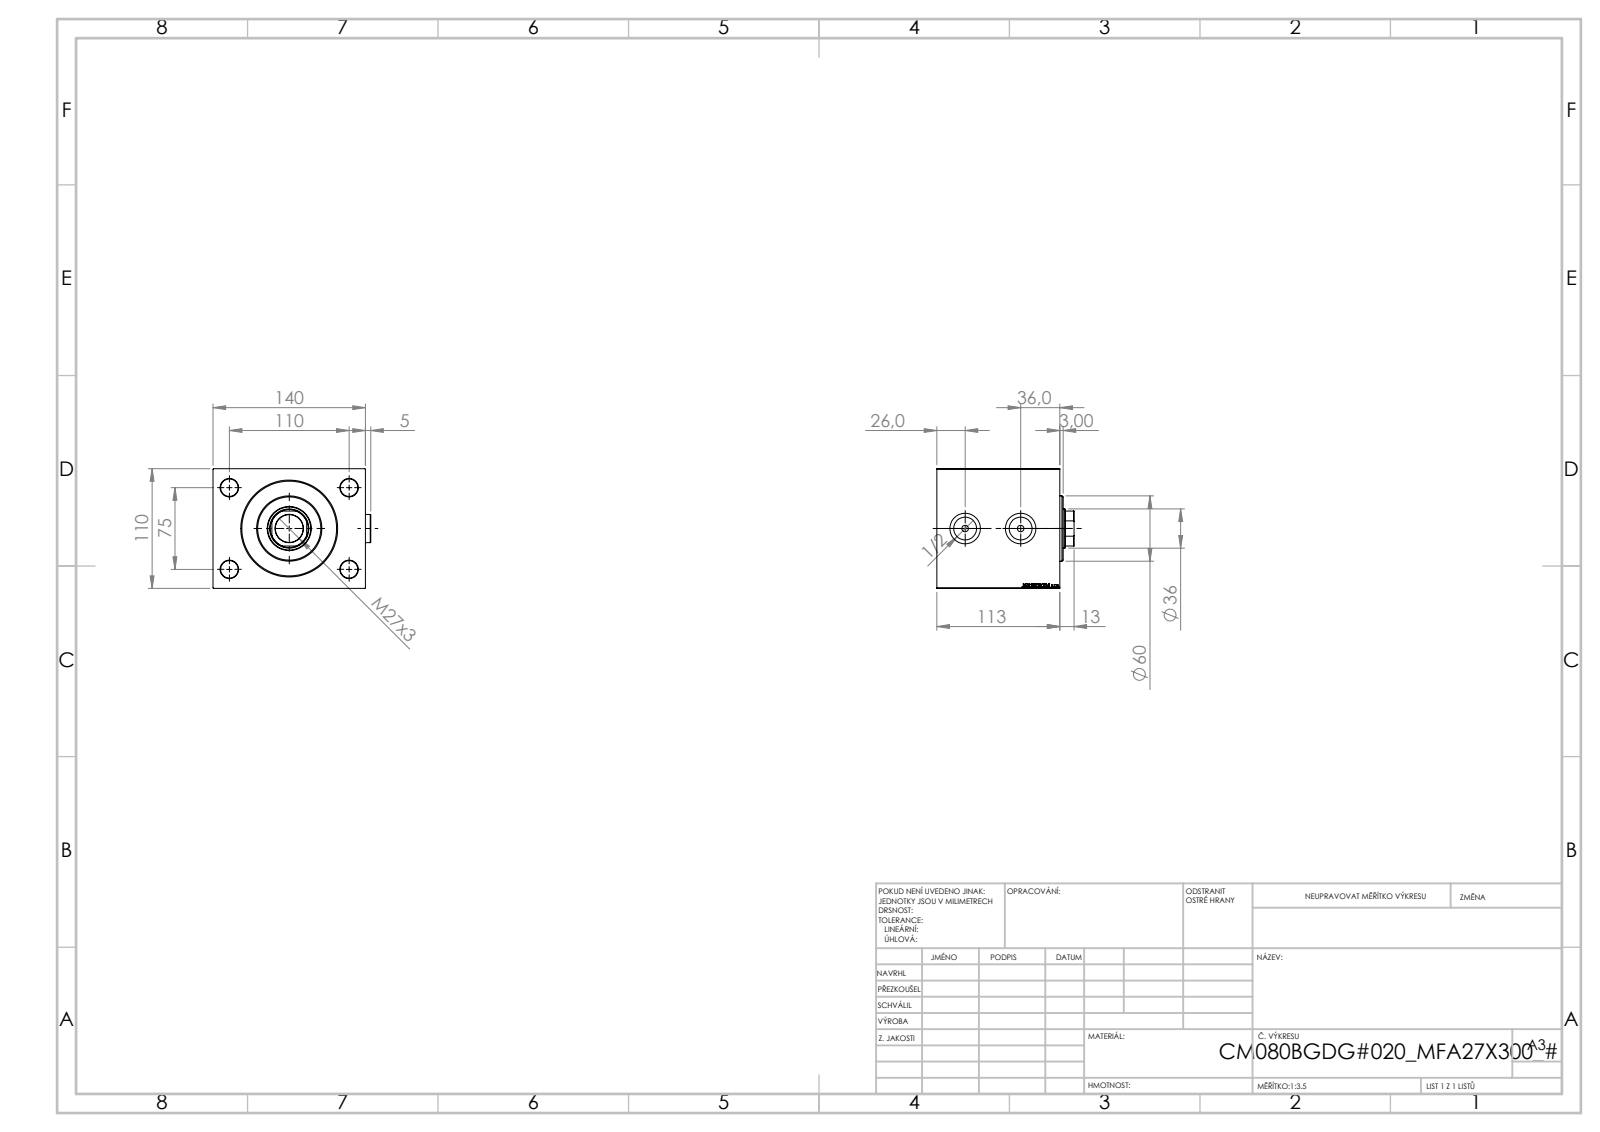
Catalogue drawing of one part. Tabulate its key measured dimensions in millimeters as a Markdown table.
| quantity | value |
| --- | --- |
| part name | V450CM_VC_B; V450CM_B_Body; Zatka_OIL_PORT; V450CM_B_VCP |
| STEP written by | SolidWorks 2019 (CONFIG_CONTROL_DESIGN) |
| units | millimeters |
| bodies | 5 solids, 936 faces (436 planar, 70 cylindrical, 430 other) |
| overall size | 144.9 × 126 × 110 |
| volume | 1 631 000 mm³ |
| surface area | 162 819 mm² |
| round holes (diameter × count) | 16 × 4, 6 × 2, 20.96 × 2, 28 × 2, 25.5 × 1, 36 × 1, 39.5 × 1, 40.5 × 1, 80 × 1, 82 × 1, 87 × 1 |
| round bosses / shafts (diameter × count) | 26 × 2, 60 × 1 |
| partial cylindrical surfaces (radius × count) | 17.5 × 1 |
| main face-to-face distances | 110, 113, 140, 51, 62, 21.6, 29.4, 91.4, 10, 31.6 |
| hole center spacings | 66.57, 75, 110, 133.14, 51 |
